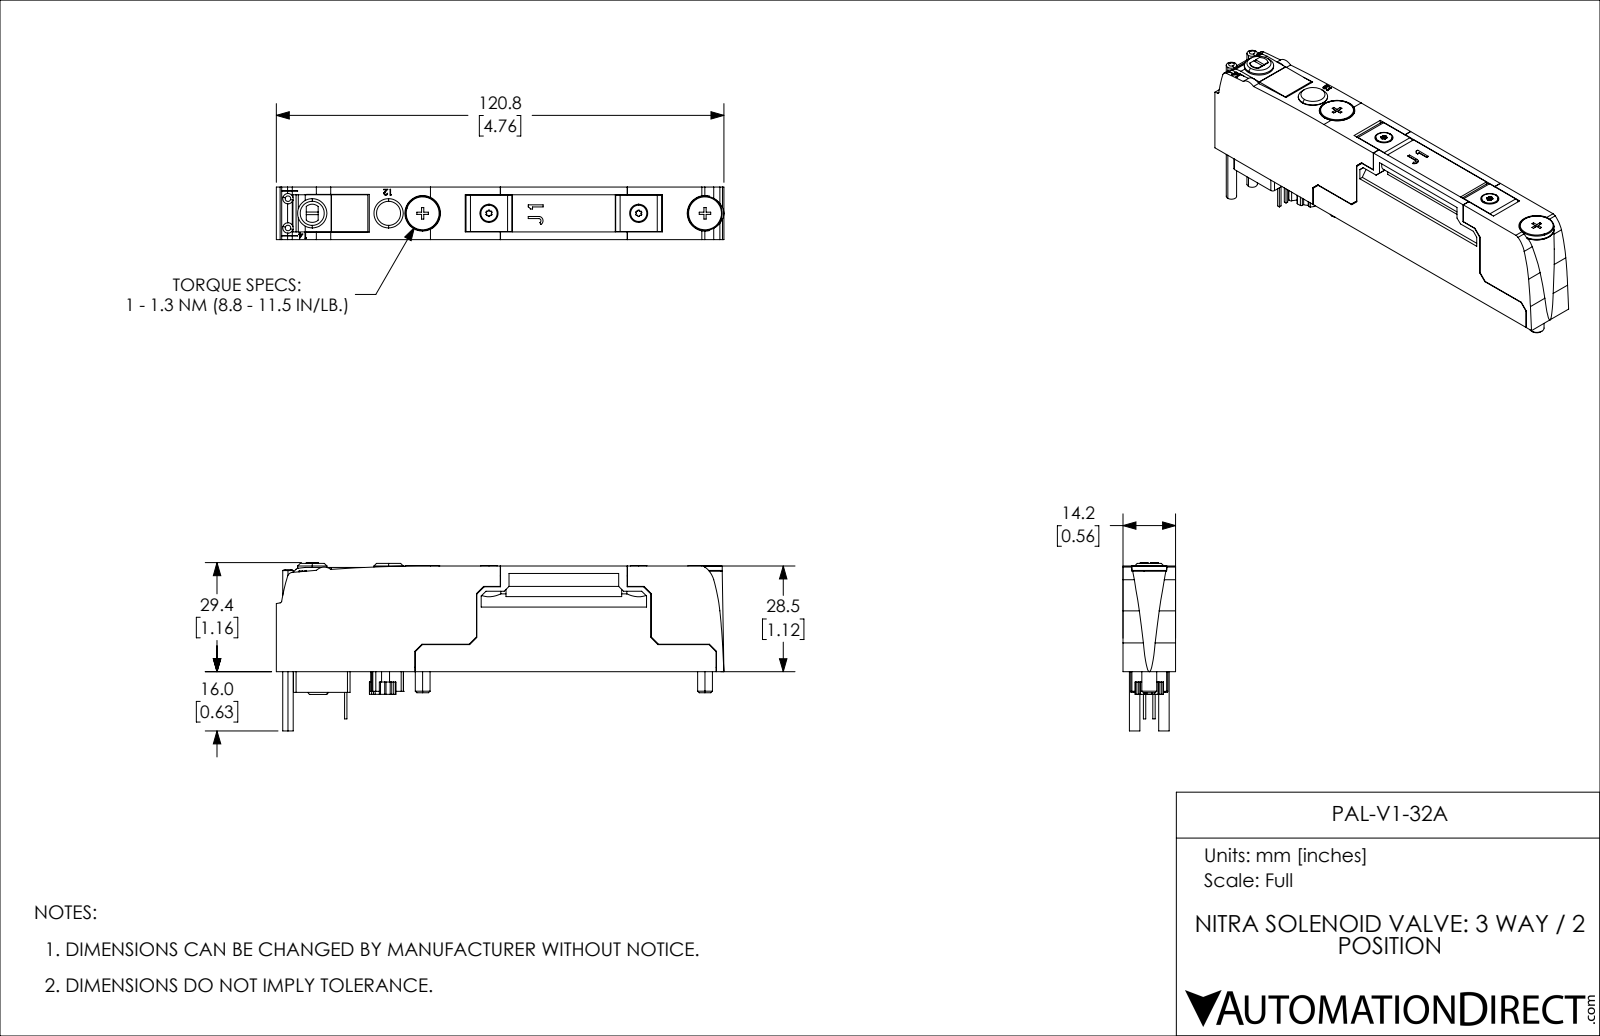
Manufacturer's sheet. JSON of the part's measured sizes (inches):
{"part_name": "PAL-V1-32A", "step_written_by": "SolidWorks 2019 (CONFIG_CONTROL_DESIGN)", "units": "inches", "bodies": {"solids": 1, "faces": 577, "planar": 395, "cylindrical": 149, "other": 33}, "overall_size": [4.756, 1.787, 0.559], "volume_in3": 2.609, "surface_area_in2": 29.08, "round_holes": [[0.165, 2], [0.122, 1], [0.378, 1]], "round_bosses_or_shafts": [[0.366, 2], [0.311, 2], [0.173, 2], [0.157, 2], [0.11, 2]], "partial_cylinders_radius": [[0.016, 12], [0.024, 6], [0.028, 4], [0.047, 4], [0.059, 3], [0.026, 2], [0.028, 2], [0.035, 2]], "face_to_face_distances": [0.559, 0.083, 0.476, 0.394, 0.087, 1.122, 0.252, 0.677, 0.835, 0.409], "hole_center_spacings": [1.11, 3, 4.11]}
